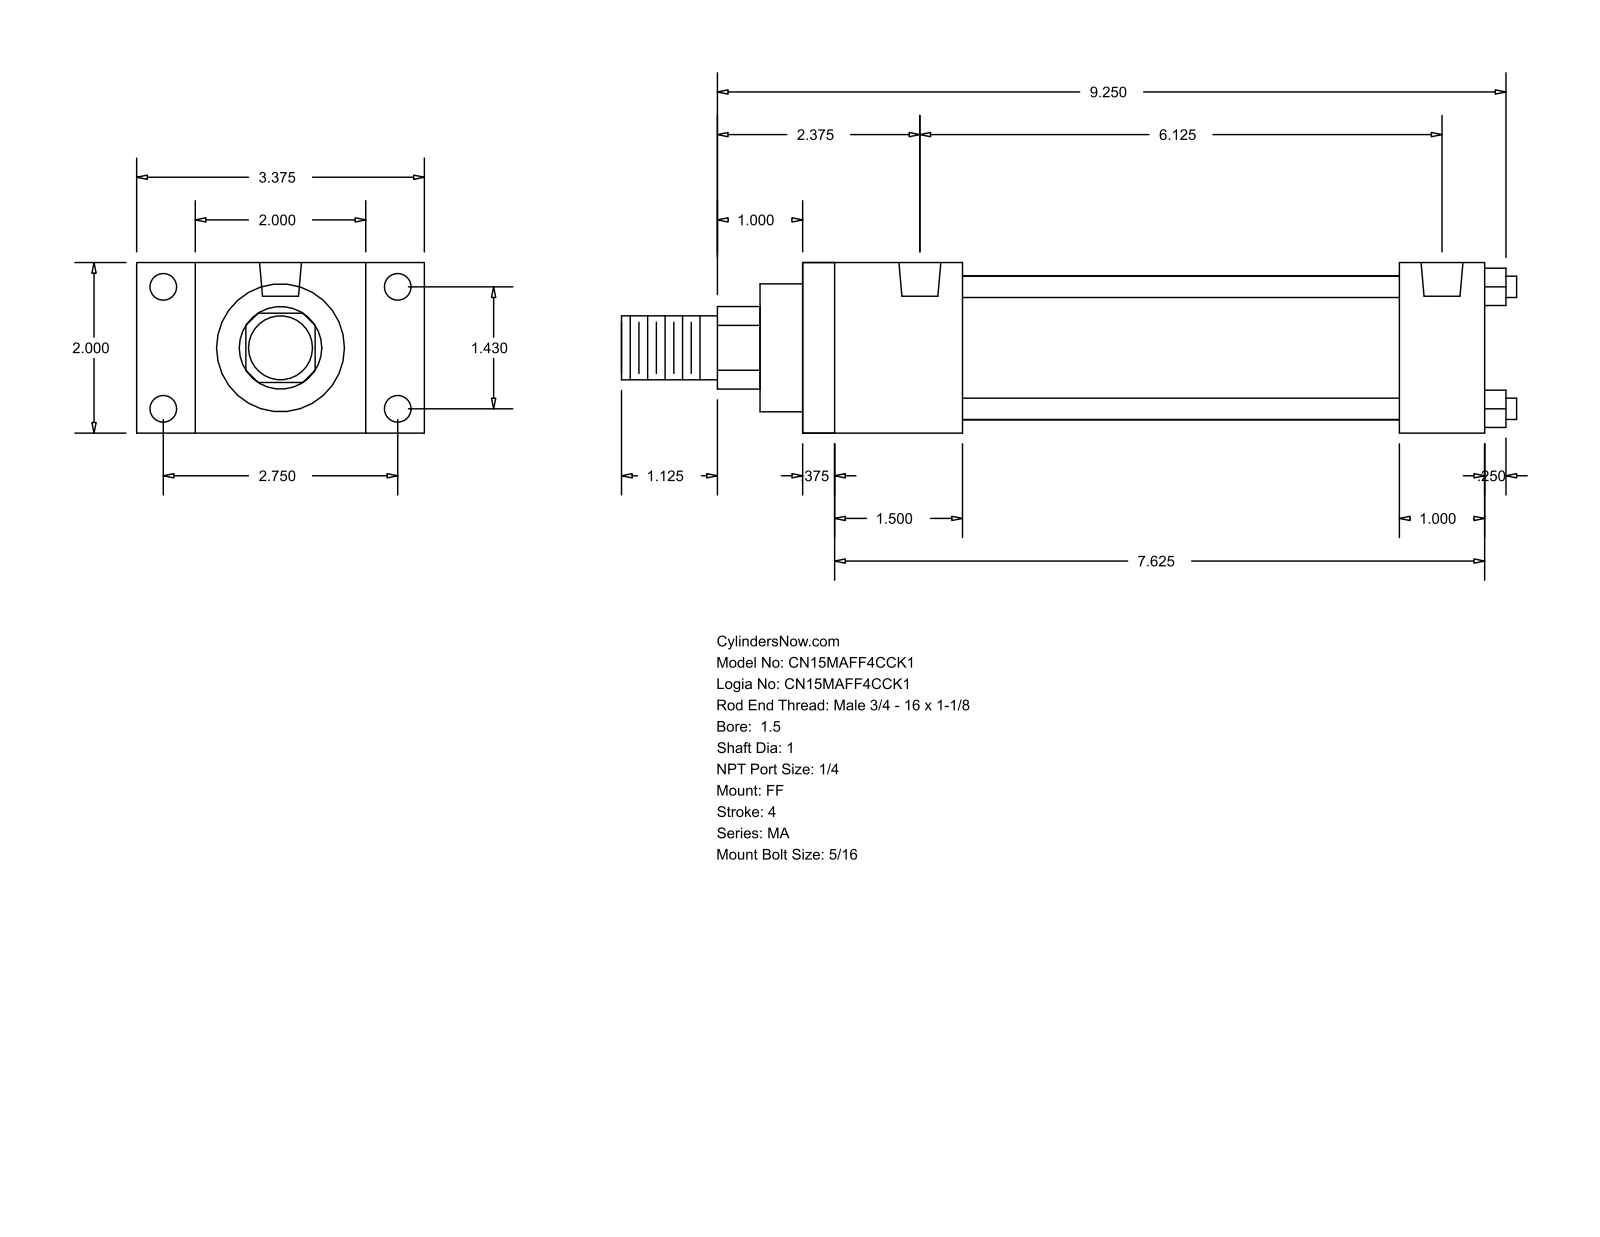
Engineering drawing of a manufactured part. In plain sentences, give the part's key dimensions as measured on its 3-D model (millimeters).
The part is named "MA_FF__0150_1". Its 3-D file was written by "GSSL Pune (CONFIG_CONTROL_DESIGN)". It is 0 solids with 92 faces: 64 planar, 28 cylindrical and 0 other. Overall it measures 266.7 by 85.72 by 50.8 millimeters. Round holes: 8 of diameter 7.94, 2 of diameter 12.49. Round bosses or shafts: 4 of diameter 6.35, 1 of diameter 42.93, 1 of diameter 38.1, 1 of diameter 25.4, 1 of diameter 19.05. Partial cylindrical surfaces (rounded edges, fillets, slot ends): 1 of radius 12.29. The main face-to-face distances are 50.8, 203.2, 9.52, 193.68, 25.4, 47.63, 177.8, 38.11, 168.28, 130.17. The hole center spacings are 36.32, 69.84, 78.72, 155.57.
